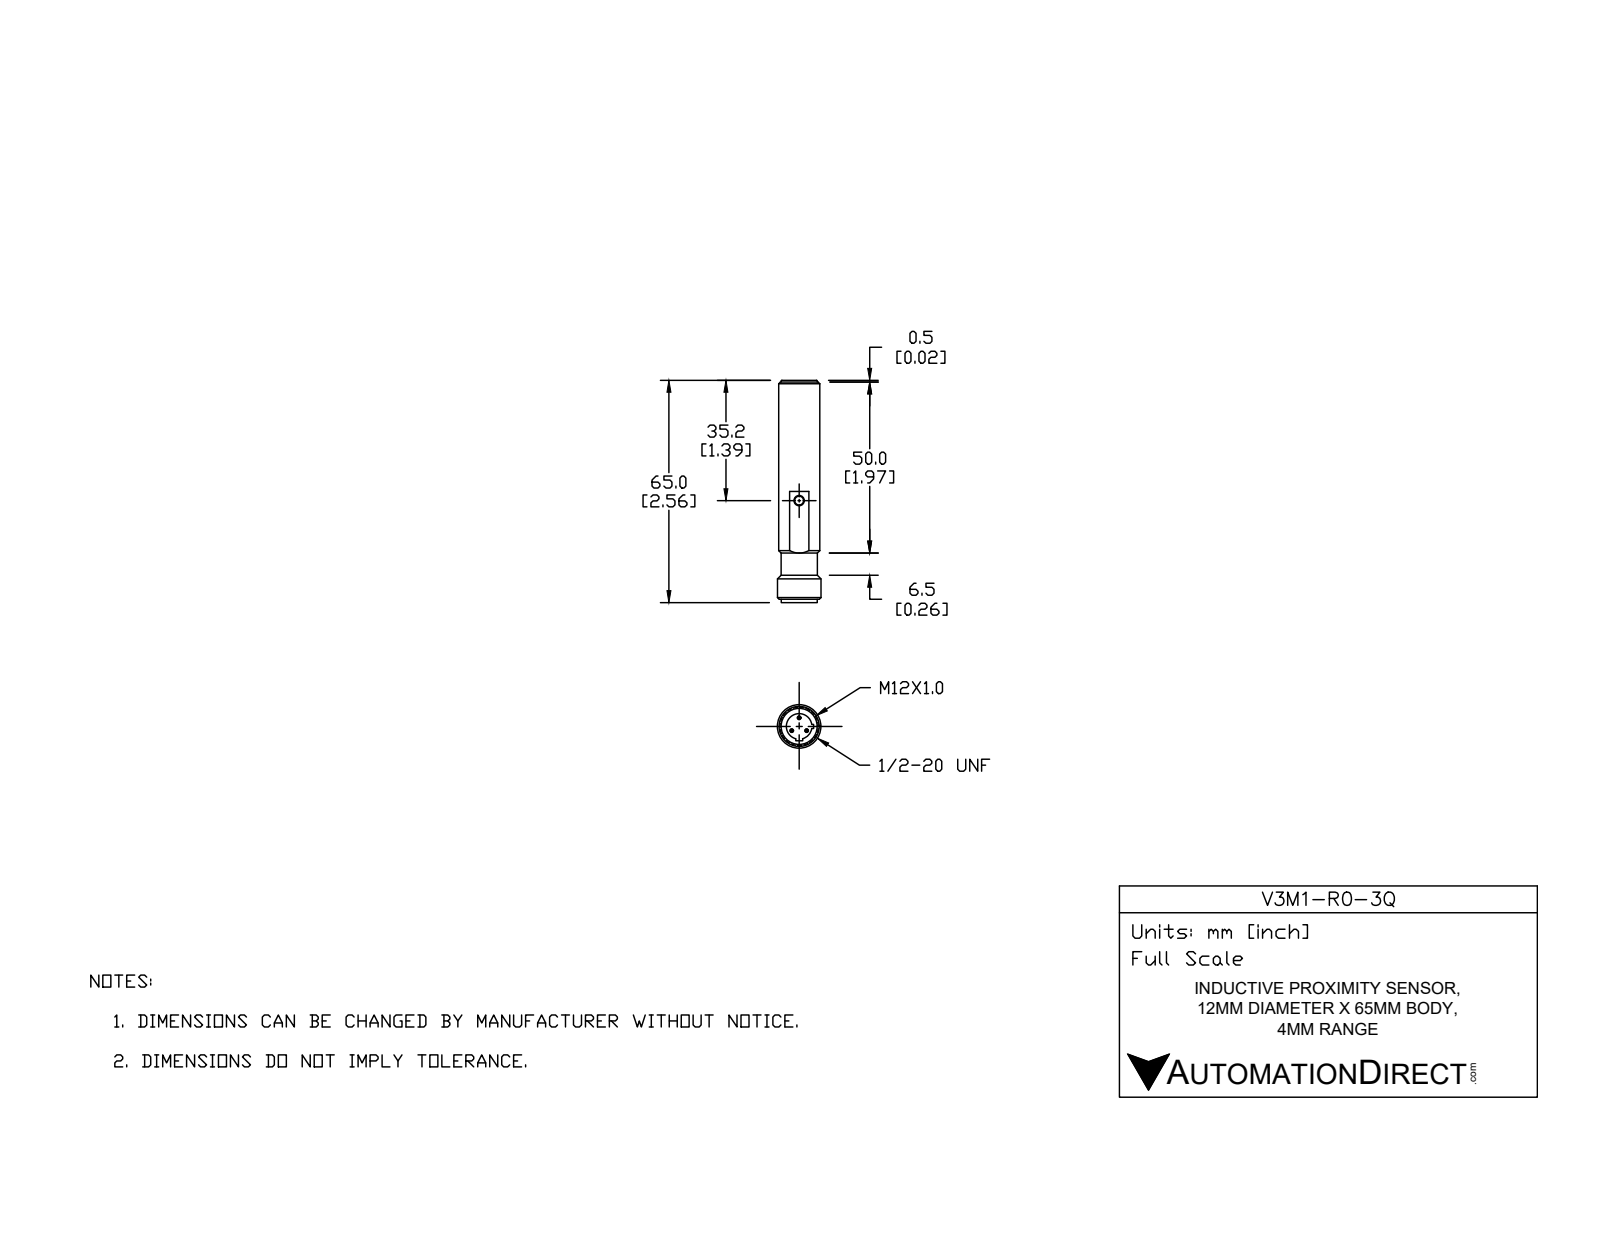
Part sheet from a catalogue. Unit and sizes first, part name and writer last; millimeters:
Units: millimetres
Overall size (bounding box): 65 × 12.7 × 12.7
Round holes (diameter × count): ⌀1 ×3, ⌀2.6 ×1, ⌀7.5 ×1, ⌀9.5 ×1
Round bosses / shafts (diameter × count): ⌀0.98 ×3, ⌀12.7 ×1, ⌀12 ×1, ⌀10.6 ×1, ⌀10.5 ×1, ⌀9.55 ×1, ⌀9.4 ×1
Main face-to-face distances: 57.9, 65, 7.1, 1, 64, 6.1, 9.5, 0.5, 57.4, 63.5
Hole centre spacings: 2.5, 4.33, 4.34
Volume: 6 831 mm³ · Surface area: 3 220 mm²
Bodies: 3 solids, 52 faces (25 planar, 17 cylindrical, 10 other)
Part name (STEP PRODUCT): V3M1_3Q_fig
STEP written by: ST-DEVELOPER v16.7 (AUTOMOTIVE_DESIGN)
